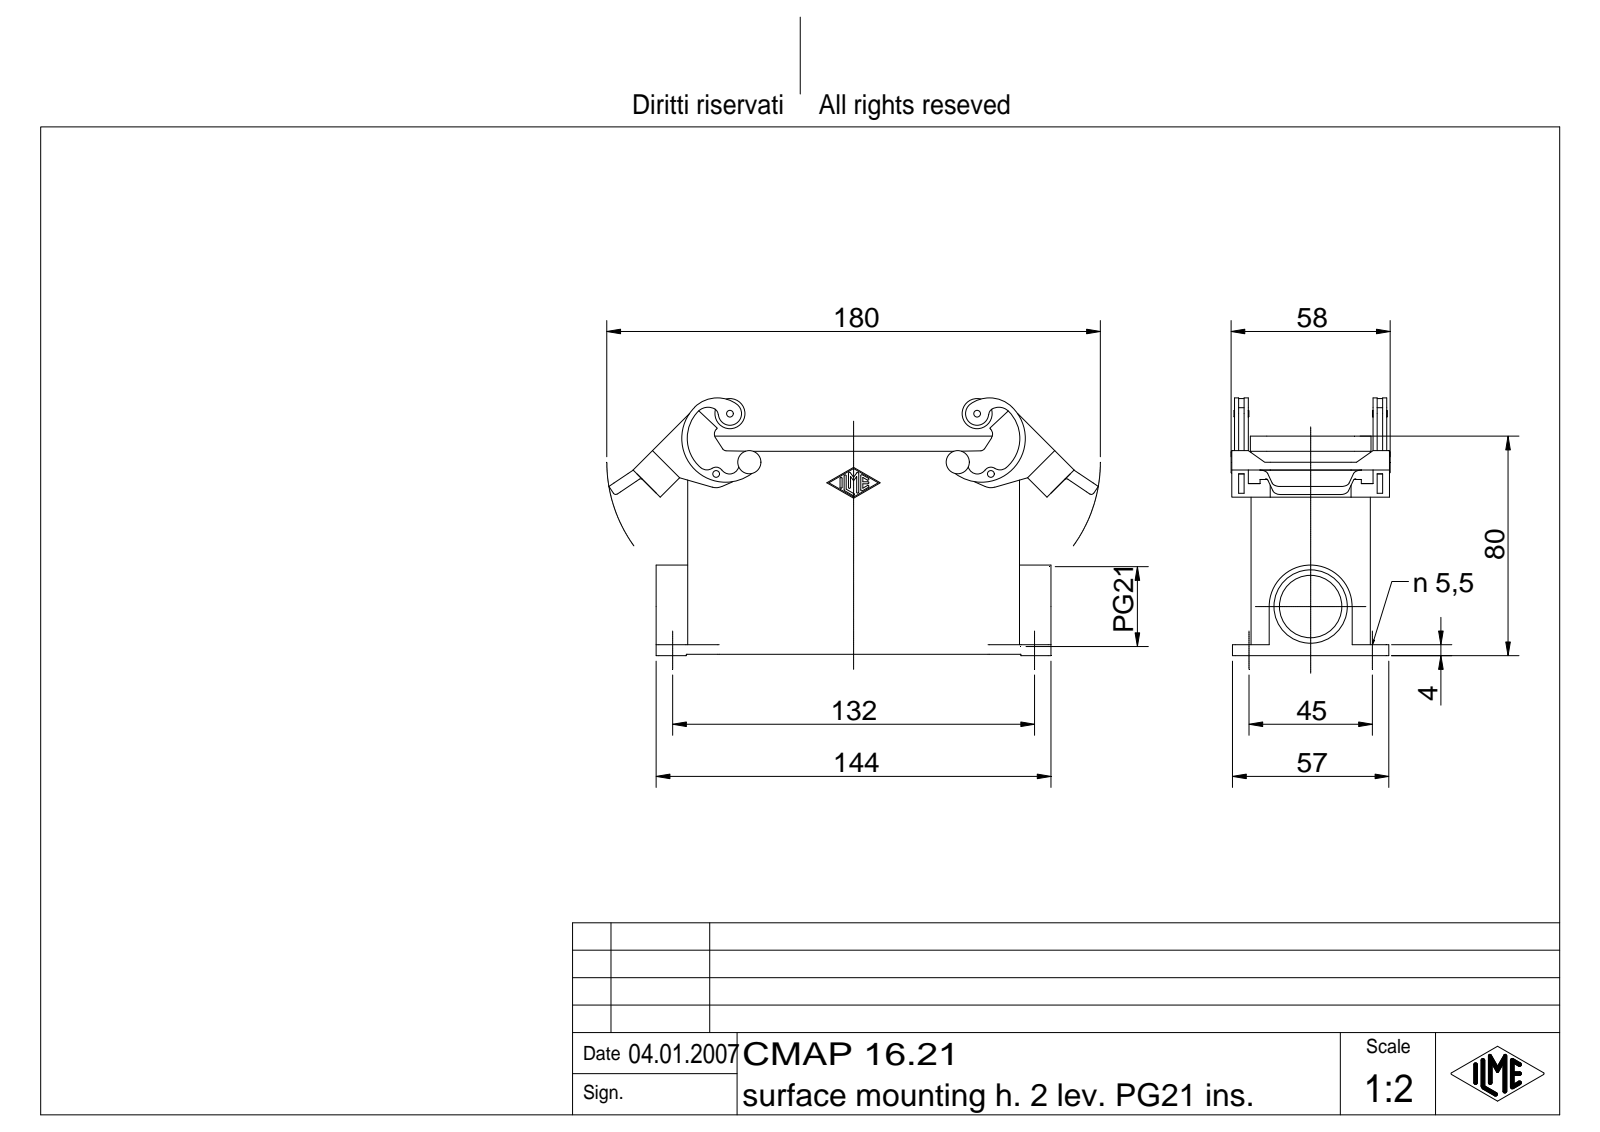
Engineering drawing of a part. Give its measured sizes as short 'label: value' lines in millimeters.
name: CMAP 16.21
written by: Autodesk Inventor 7 (AUTOMOTIVE_DESIGN)
unit: mm
bodies: 1 solid, 749 faces (191 planar, 205 cylindrical, 353 other)
size: 178.49 × 93.94 × 58
volume: 146 602 mm³; area: 81 249 mm²
holes: 4× ⌀2, 4× ⌀5.5, 2× ⌀2.5, 1× ⌀22.78, 1× ⌀26.78
bosses: 2× ⌀11, 2× ⌀5, 2× ⌀3
rounds: 20× R1, 14× R0.38, 12× R3, 8× R6, 6× R2.5, 4× R1.5, 4× R2, 4× R3.5
face distances: 3, 40.5, 43.5, 37.5, 3.5, 4, 0.75, 50.5, 40.75, 3.75
hole spacings: 22.56, 45, 97.67, 132, 139.46, 90.14, 100.18
